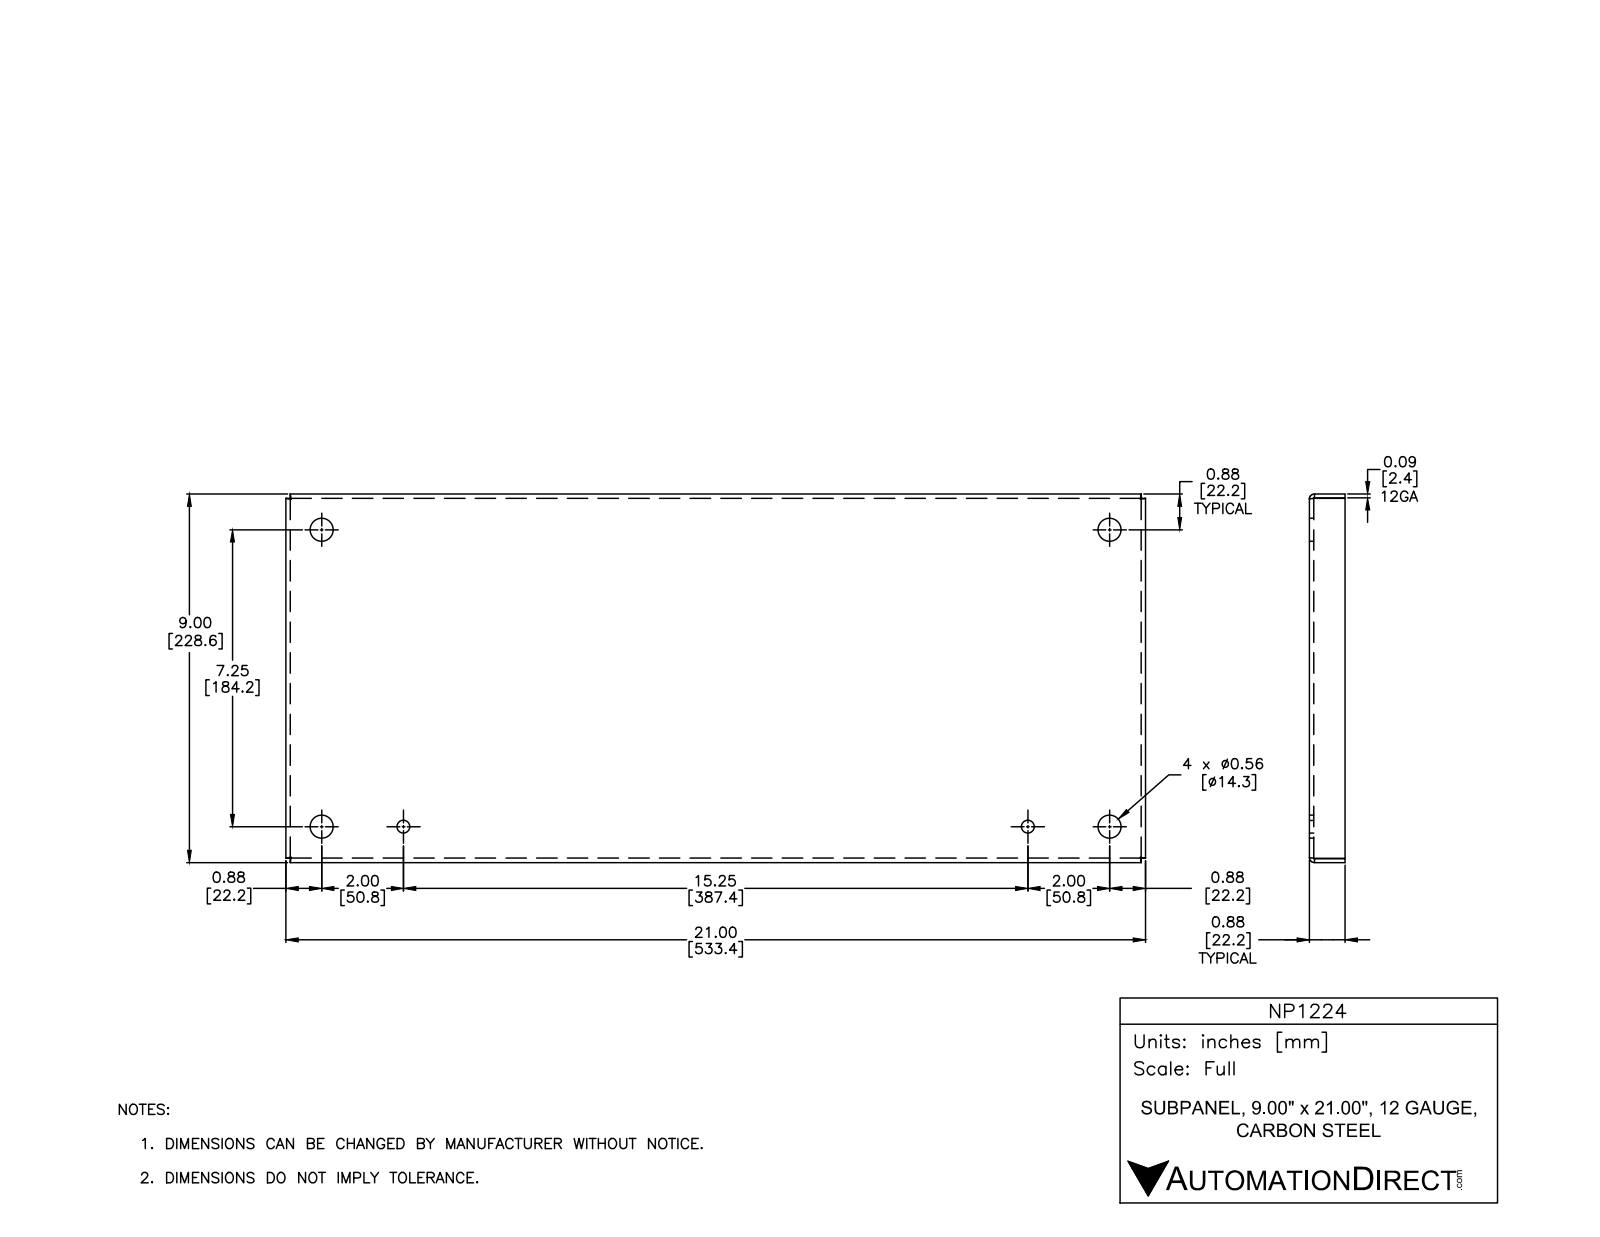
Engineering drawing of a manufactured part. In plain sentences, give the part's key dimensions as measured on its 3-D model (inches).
The part is named "NP1224". Its 3-D file was written by "Autodesk Inventor 2012 (AUTOMOTIVE_DESIGN)". It is 1 solid with 44 faces: 22 planar, 14 cylindrical and 8 other. Overall it measures 21 by 9 by 0.875 inches. Its volume is 21.75 cubic inches and its surface area 471.1 square inches. Round holes: 4 of diameter 0.563, 2 of diameter 0.312. Partial cylindrical surfaces (rounded edges, fillets, slot ends): 4 of radius 0.031, 4 of radius 0.125. The main face-to-face distances are 0.094, 8.906, 9, 8.813, 20.906, 21, 20.813, 0.781, 0.875, 0.105. The hole center spacings are 7.25, 7.521, 18.712, 19.25, 20.57, 2, 2, 15.25.
